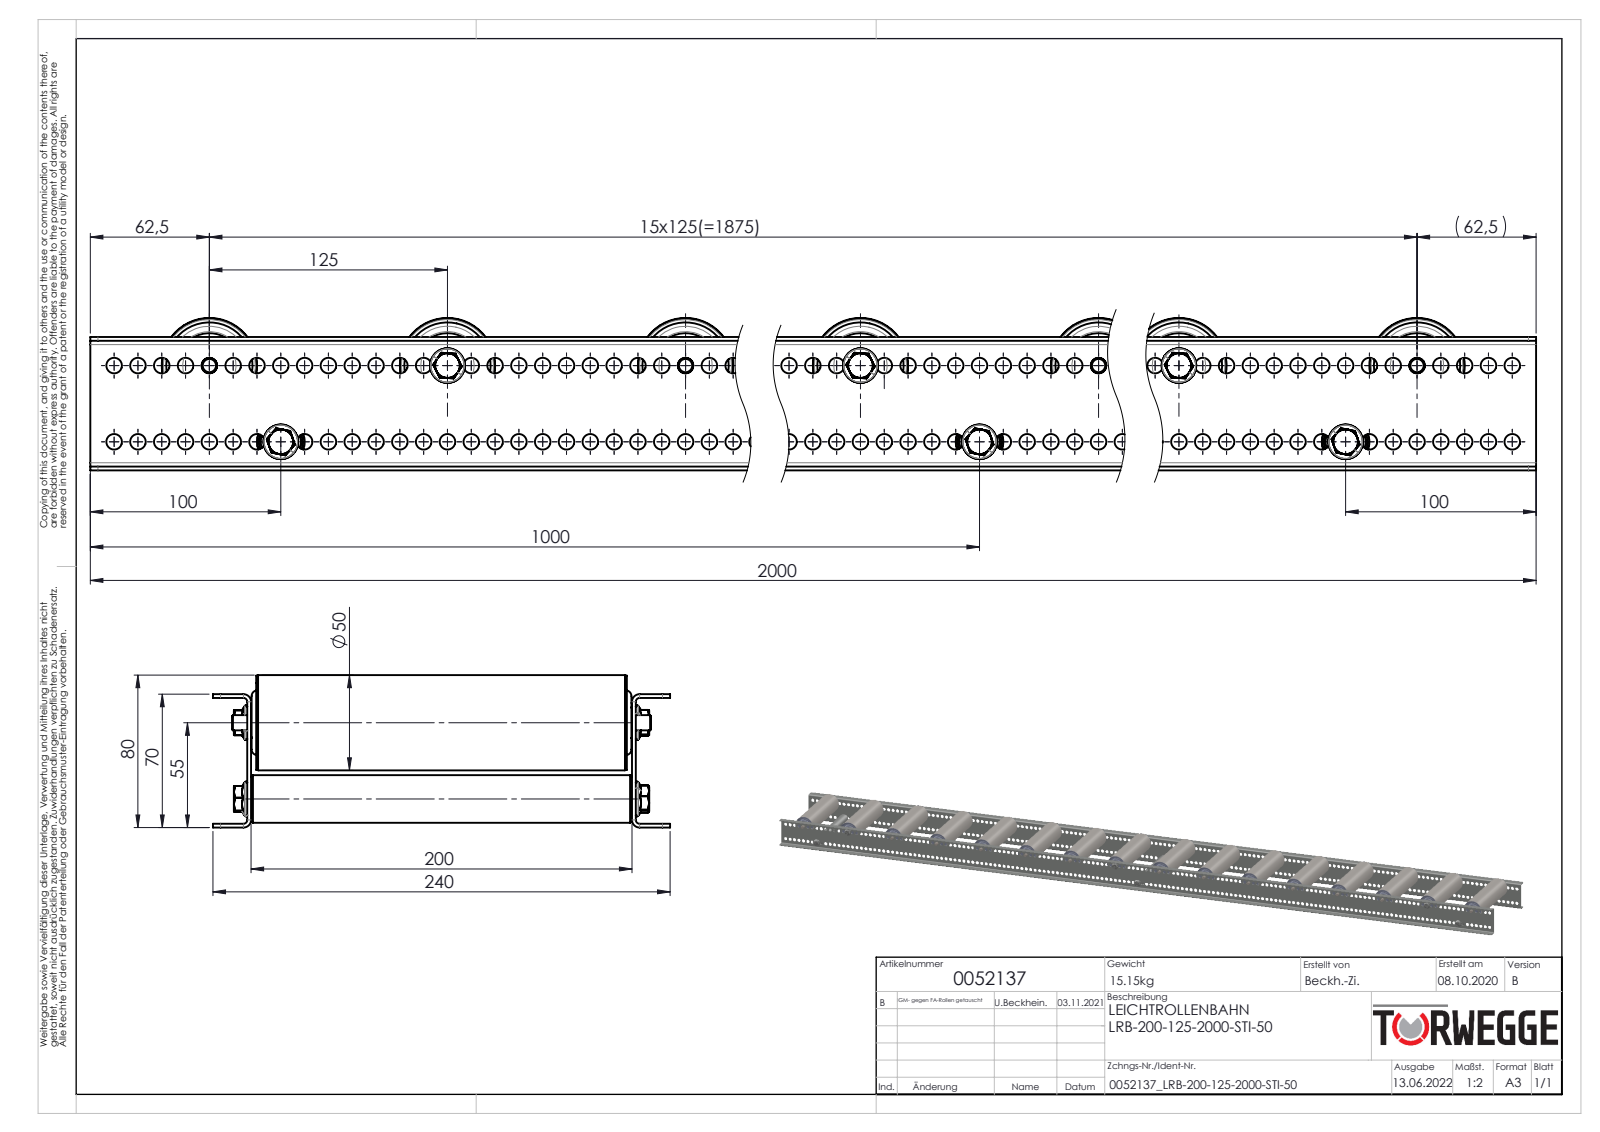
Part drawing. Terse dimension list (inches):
name: 0026293_Typ-TRG-50x1,5-12; 0039771_Tragrollenrohr-Ø50x1,5STI_KFG_EL200; Profil_LRB-20x70x20x2_KFG_S100202_U-PROFIL-20-70-20-2-LRB-L=2000; 0026295_Typ-TRG_50x1,5-8 (+8 more)
written by: SolidWorks 2020 (AUTOMOTIVE_DESIGN)
unit: in
bodies: 392 solids, 7558 faces (1452 planar, 2944 cylindrical, 3162 other)
size: 78.74 × 9.449 × 3.15
volume: 127.8 in³; area: 3 757 in²
holes: 318× ⌀0.323, 16× ⌀0.673, 16× ⌀0.728, 16× ⌀1.091, 16× ⌀1.783, 16× ⌀1.85, 13× ⌀0.299, 6× ⌀0.268, 3× ⌀0.472, 3× ⌀0.48, 3× ⌀0.756, 3× ⌀0.827
bosses: 19× ⌀0.315, 16× ⌀1.969, 16× ⌀1.949, 16× ⌀1.862, 16× ⌀1.169, 16× ⌀1.079, 16× ⌀1.075, 16× ⌀0.63
rounds: 26× R0.024, 26× R0.03, 26× R0.096, 13× R0.192, 13× R0.276, 12× R0.098, 8× R0.157, 4× R0.079
face distances: 0.079, 7.953, 2.677, 7.874, 8.031, 2.756, 2.598, 0.039, 0.787, 0.709
hole spacings: 0.492, 0.984, 1.476, 1.969, 2.461, 2.953, 3.445, 3.937
